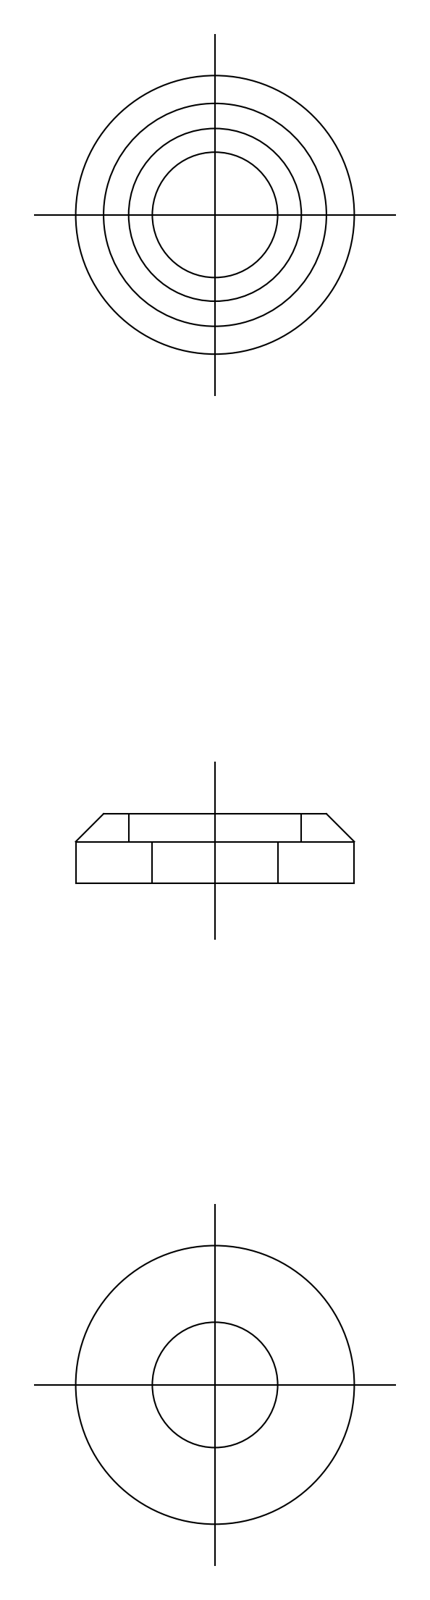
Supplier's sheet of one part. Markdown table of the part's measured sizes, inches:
| quantity | value |
| --- | --- |
| part name | facing ring |
| STEP written by | CADfix (AUTOMOTIVE_DESIGN) |
| units | inches |
| bodies | 1 solid, 11 faces (0 planar, 0 cylindrical, 11 other) |
| overall size | 0.394 × 0.394 × 0.098 |
| volume | 0.008 in³ |
| surface area | 0.349 in² |
